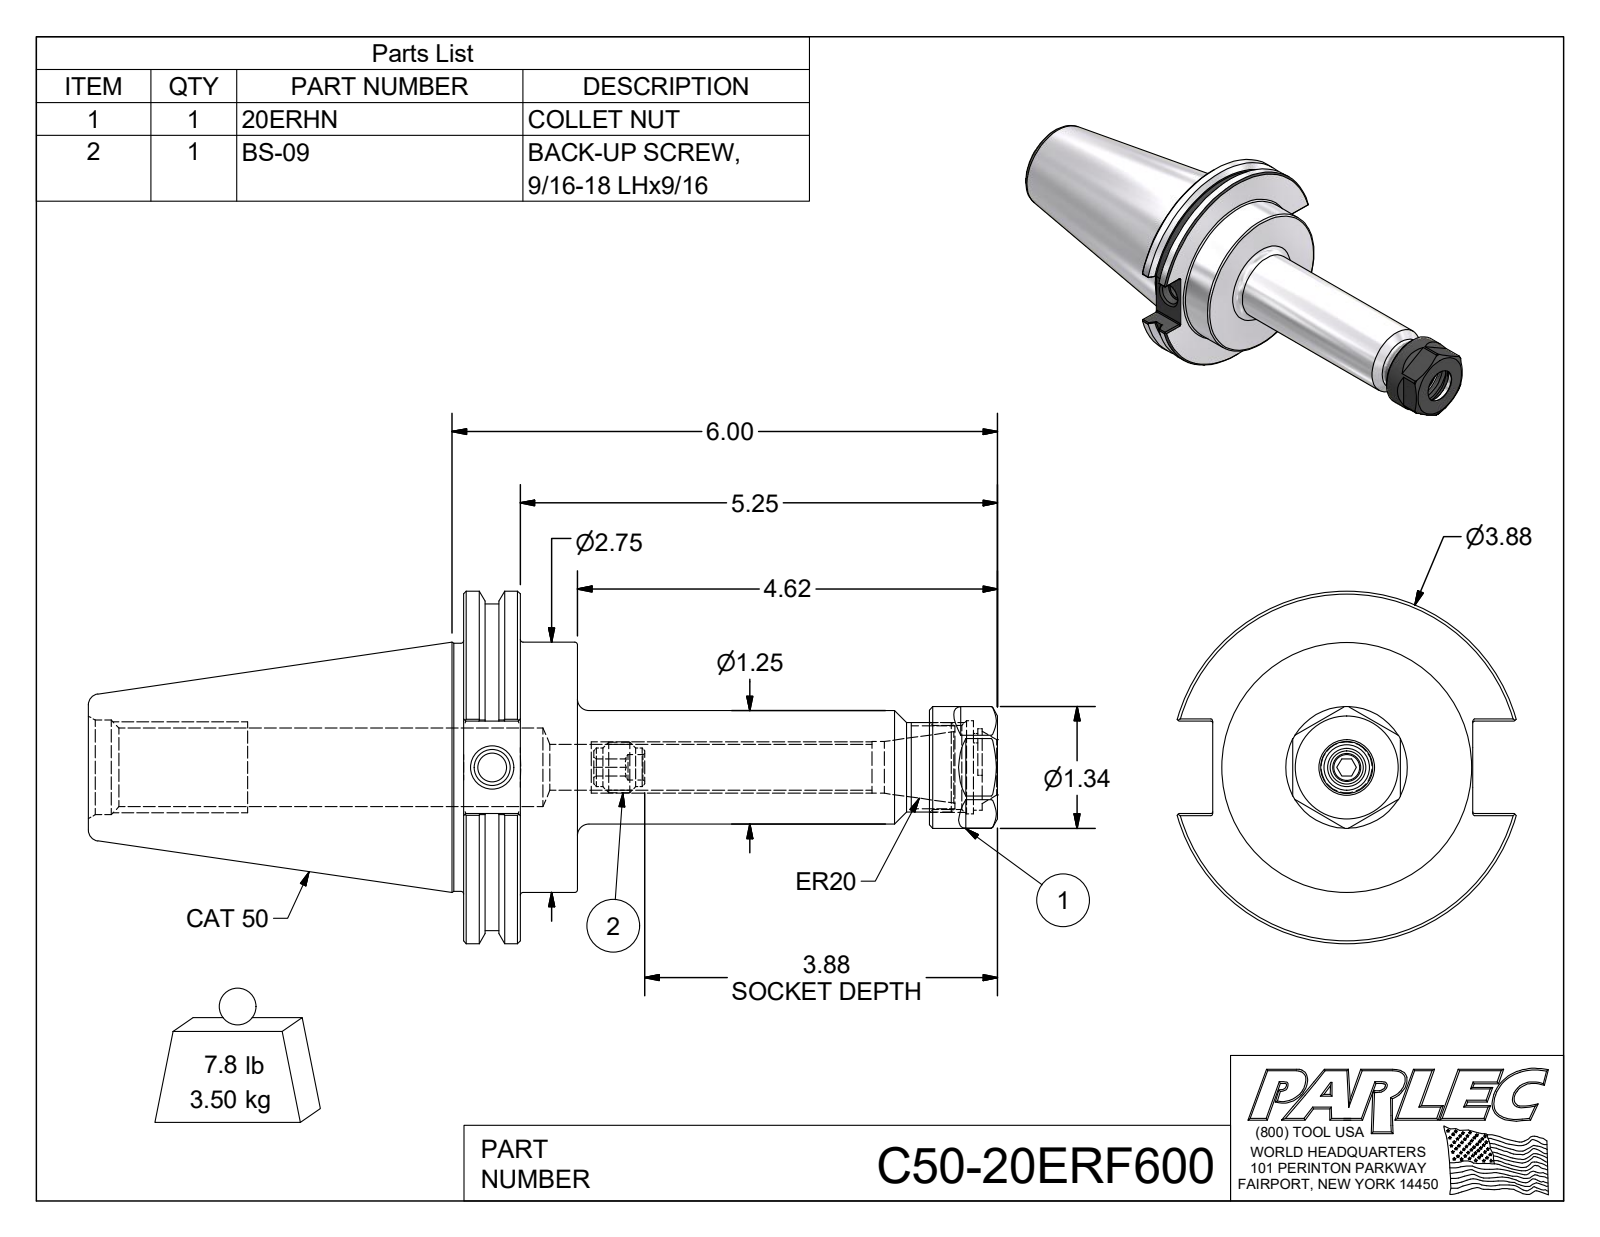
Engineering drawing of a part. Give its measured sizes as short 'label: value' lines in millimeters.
name: C50-20ER6-1; 20ERHN; BS-09; C50-20ERF600
written by: Autodesk Inventor 2016 (AUTOMOTIVE_DESIGN)
unit: mm
bodies: 3 solids, 152 faces (64 planar, 39 cylindrical, 49 other)
size: 254 × 98.42 × 94.71
volume: 447 865 mm³; area: 68 352 mm²
holes: 1× ⌀7.14, 1× ⌀8, 1× ⌀10.13, 1× ⌀12.75, 1× ⌀14.48, 1× ⌀15.49, 1× ⌀21.97, 1× ⌀23.5, 1× ⌀26, 1× ⌀26.37
bosses: 1× ⌀98.42, 1× ⌀91.29, 1× ⌀69.85, 1× ⌀69.34, 1× ⌀34, 1× ⌀31.75, 1× ⌀25, 1× ⌀14.1
rounds: 12× R0.51, 1× R9.47, 1× R10.55, 1× R10.75
face distances: 15.88, 31.88, 16, 149.23, 133.35, 117.35, 30, 104.77, 120.65, 136.65
